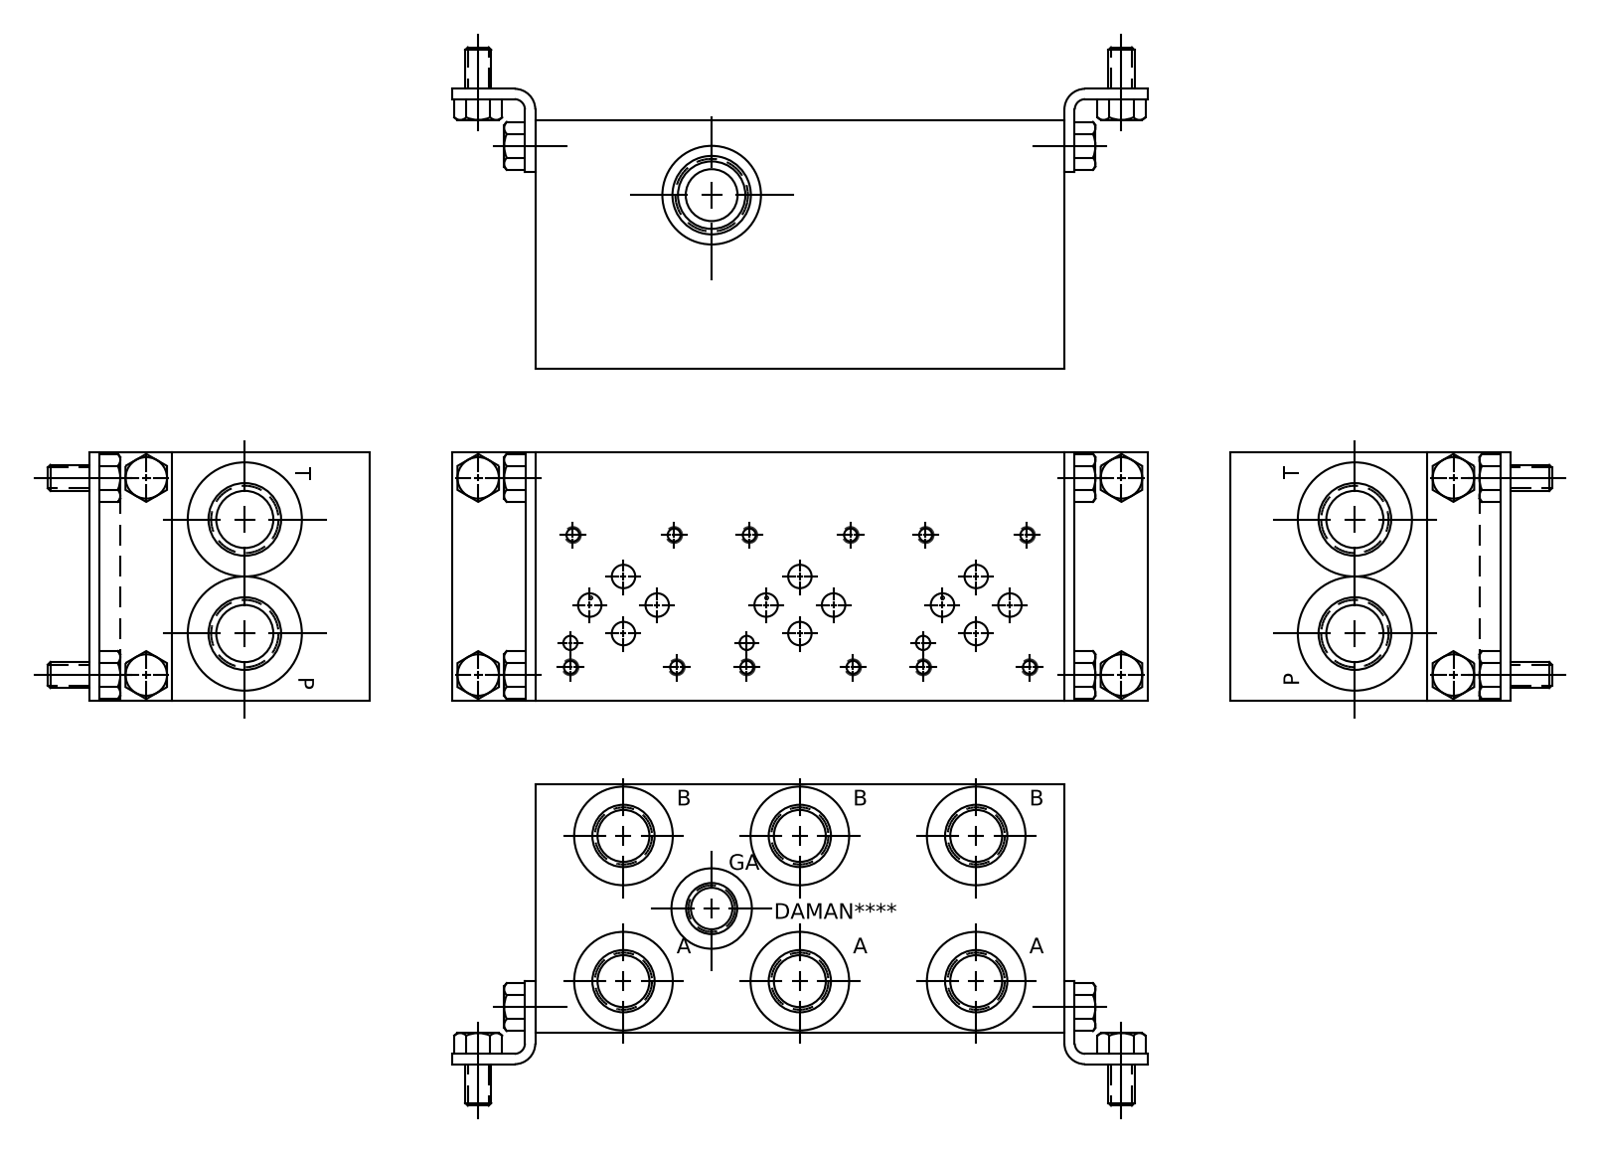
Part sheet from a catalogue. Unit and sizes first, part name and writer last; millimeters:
Units: millimetres
Overall size (bounding box): 161.93 × 76.2 × 76.2
Round holes (diameter × count): ⌀3.78 ×12, ⌀4.83 ×12, ⌀7.14 ×9, ⌀17.5 ×8, ⌀19.05 ×8, ⌀19.25 ×8, ⌀30.63 ×8, ⌀14.3 ×6, ⌀3.96 ×3, ⌀6.35 ×3, ⌀6.53 ×2, ⌀7.92 ×2
Main face-to-face distances: 76.2, 0.79, 161.93, 75.41, 161.14, 160.35, 15.06, 14.27, 61.14, 15.02
Hole centre spacings: 107.95, 53.97, 53.98, 19.95, 22.05, 33.55, 40.49, 51.45
Volume: 849 738 mm³ · Surface area: 83 160 mm²
Bodies: 1 solid, 788 faces (399 planar, 108 cylindrical, 281 other)
Part name (STEP PRODUCT): Part_DD03P032S~C_3D
STEP written by: Autodesk Inventor 2020 (CONFIG_CONTROL_DESIGN)
